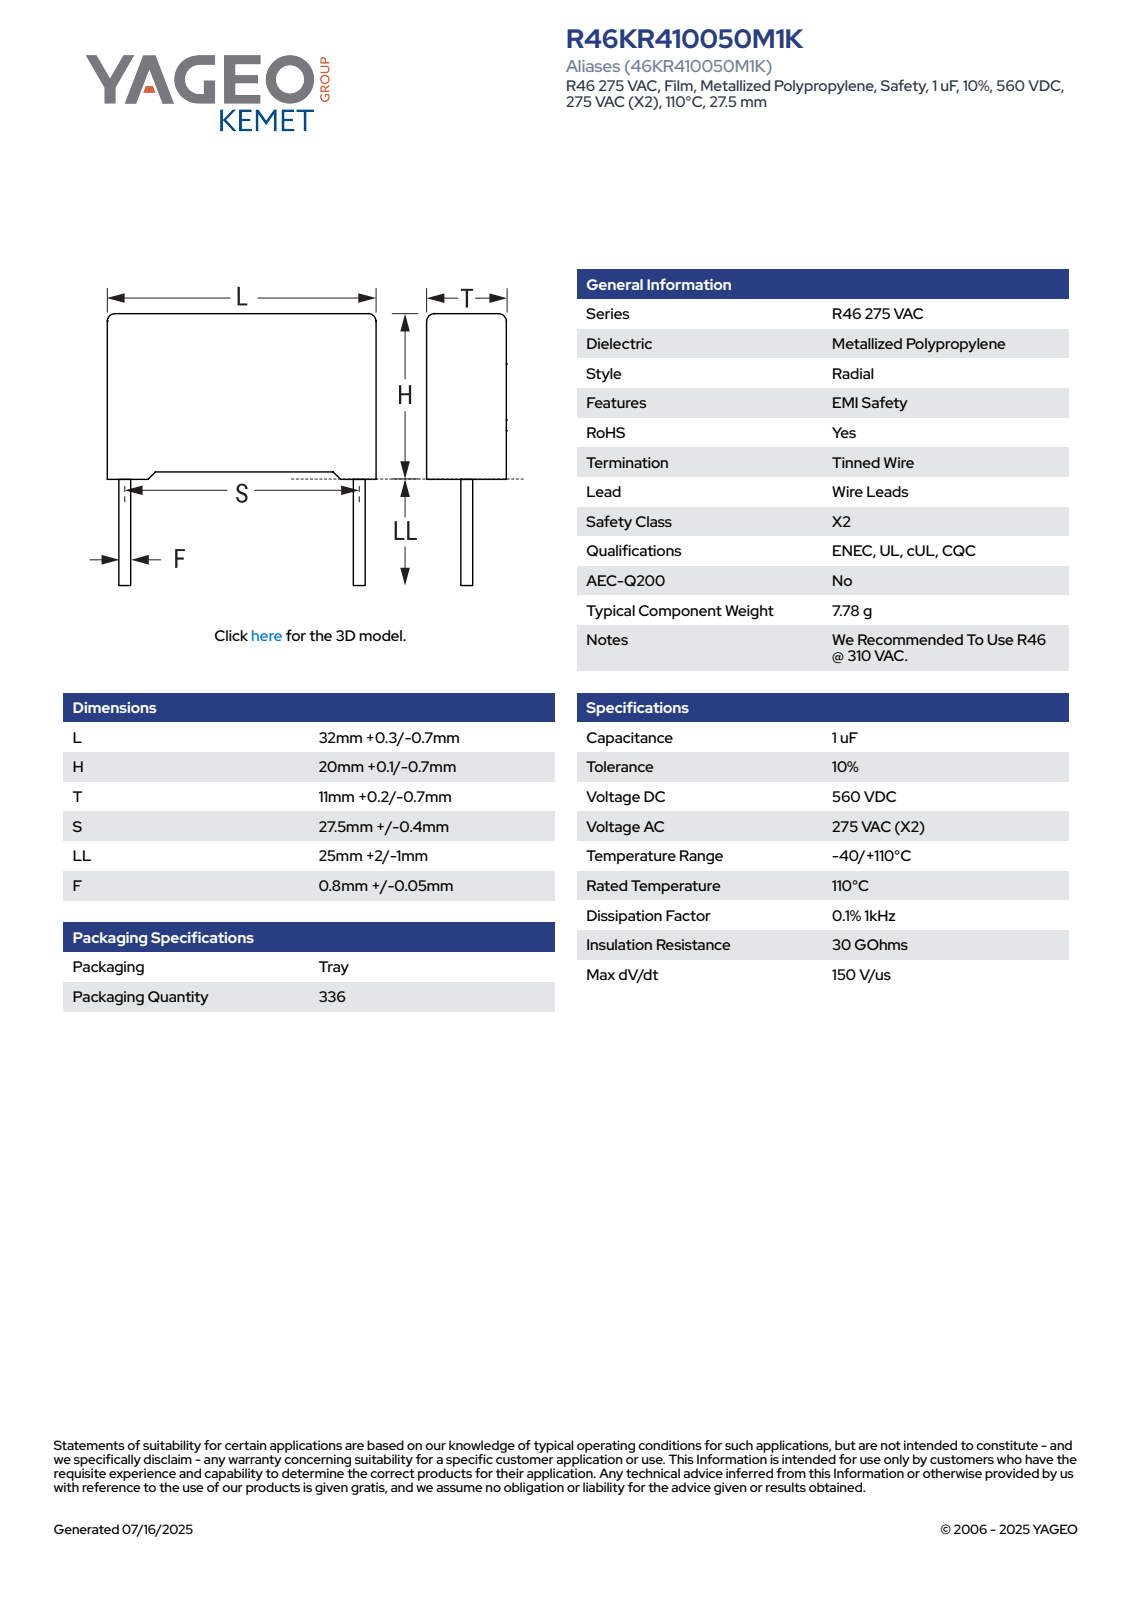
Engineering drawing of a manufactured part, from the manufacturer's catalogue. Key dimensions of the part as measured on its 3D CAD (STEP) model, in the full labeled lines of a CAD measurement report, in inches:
Part name (STEP PRODUCT): CFR_RB2_32X20X11_L32.3H20.1T11.2S27.5LL27F0.85
STEP written by: SolidWorks 2021 (AUTOMOTIVE_DESIGN)
Units: inches
Bodies: 4 solids, 85 faces (77 planar, 8 cylindrical, 0 other)
Overall size (bounding box): 1.854 × 1.272 × 0.441
Volume: 0.431 in³ · Surface area: 4.145 in²
Round bosses / shafts (diameter × count): ⌀0.033 ×2
Partial cylindrical surfaces — rounded edges, fillets, slot ends (radius × count): R0.02 ×4
Main face-to-face distances: 0.441, 0.762, 1.272, 0.764, 0.027, 0.03, 0.791, 0.043, 0.441, 1.229
